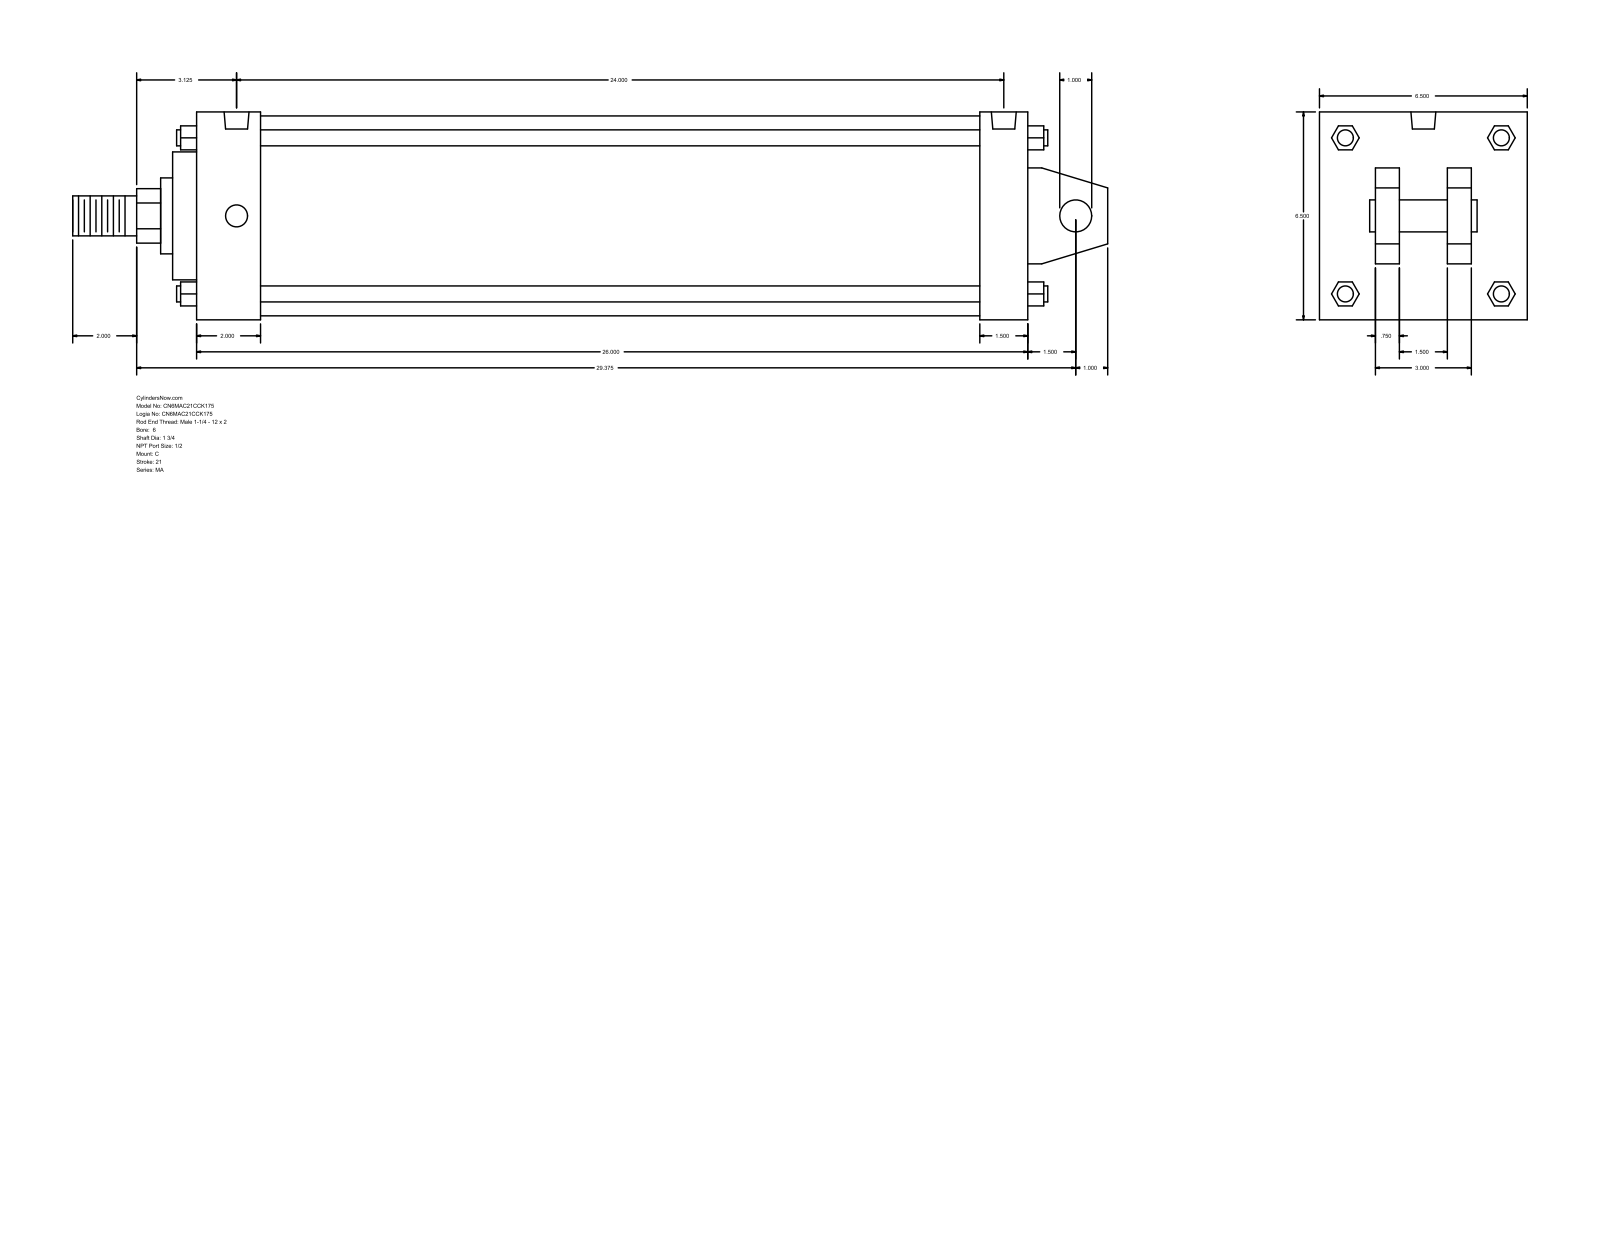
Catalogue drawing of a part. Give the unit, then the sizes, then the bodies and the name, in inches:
Units: inches
Overall size (bounding box): 32.375 × 6.5 × 6.5
Round holes (diameter × count): ⌀0.687 ×4, ⌀0.778 ×2
Round bosses / shafts (diameter × count): ⌀0.5 ×4, ⌀6.25 ×1, ⌀4 ×1, ⌀2.375 ×1, ⌀1.75 ×1, ⌀1.25 ×1, ⌀1 ×1
Partial cylindrical surfaces — rounded edges, fillets, slot ends (radius × count): R0.852 ×1
Main face-to-face distances: 6.5, 26, 0.75, 1.5, 2.5, 4, 1.75, 4.75, 2.25, 2
Hole centre spacings: 24
Bodies: 0 solids, 141 faces (109 planar, 32 cylindrical, 0 other)
Part name (STEP PRODUCT): MA_C__0600_1.75
STEP written by: GSSL Pune (CONFIG_CONTROL_DESIGN)
